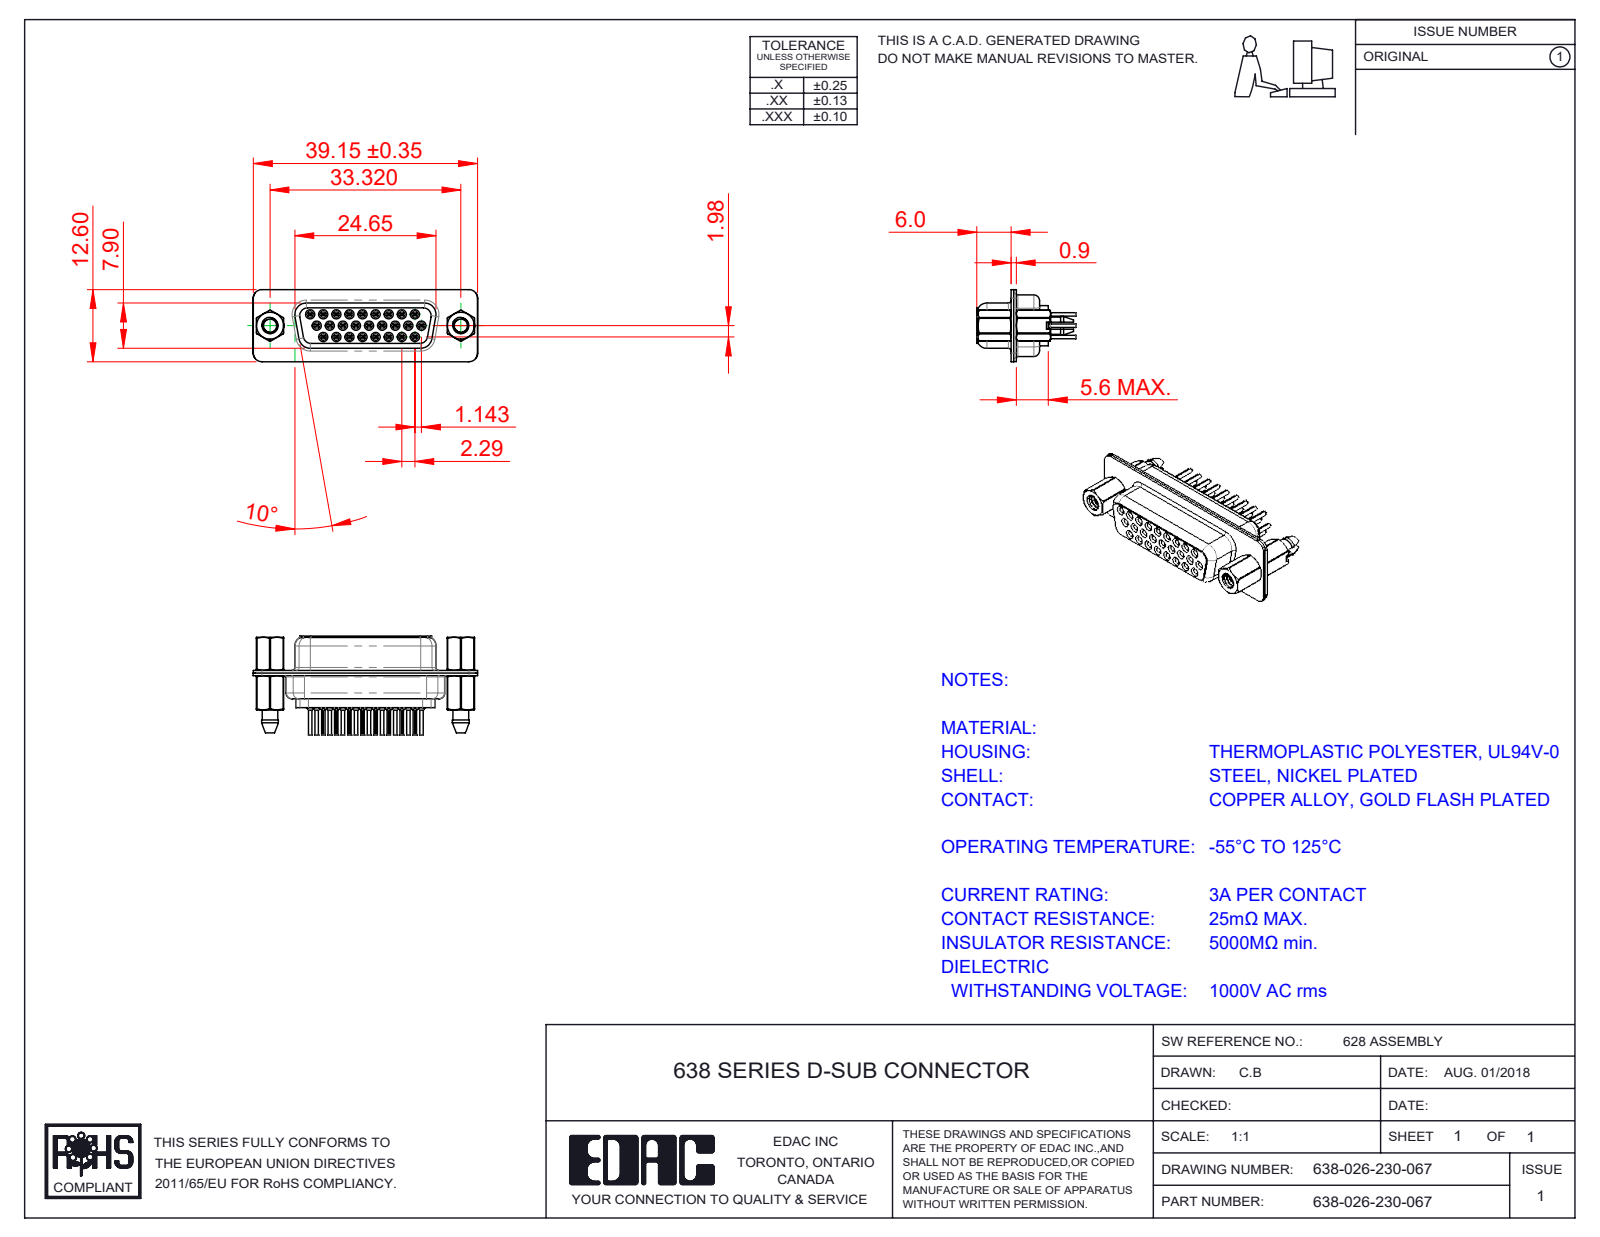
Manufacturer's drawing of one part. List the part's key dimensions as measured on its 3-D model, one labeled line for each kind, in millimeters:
Part name (STEP PRODUCT): 638 4-40 Hex Standoff; 638 Contact Row 1_30; 638 Contact Row 2_30; 638 4-40 Threaded Boardlock_LP (+5 more)
STEP written by: SolidWorks 2020 (CONFIG_CONTROL_DESIGN)
Units: millimetres
Bodies: 33 solids, 3781 faces (927 planar, 1099 cylindrical, 1755 other)
Overall size (bounding box): 39.19 × 17.3 × 12.6
Volume: 2 538 mm³ · Surface area: 9 075 mm²
Round holes (diameter × count): ⌀0.2 ×26, ⌀0.8 ×26, ⌀1 ×26, ⌀1.1 ×26, ⌀1.6 ×26, ⌀1.7 ×26, ⌀1.8 ×26, ⌀2.26 ×2, ⌀2.29 ×2, ⌀4 ×2, ⌀4.05 ×2, ⌀4.85 ×2
Round bosses / shafts (diameter × count): ⌀2 ×26, ⌀1.5 ×26, ⌀1.2 ×26, ⌀0.6 ×26, ⌀4.95 ×2, ⌀4.8 ×2, ⌀2.79 ×2
Partial cylindrical surfaces — rounded edges, fillets, slot ends (radius × count): R0.1 ×52, R1.5 ×22, R0.28 ×18, R2 ×12, R1.55 ×8, R1.35 ×5, R0.25 ×4, R0.5 ×4
Main face-to-face distances: 0.45, 0.4, 1.43, 8.88, 6.6, 0.9, 4.76, 2.28, 1.4, 0.85
Hole centre spacings: 3.96, 2.28, 4.57, 6.05, 2.29, 8.24, 6.86, 10.48
